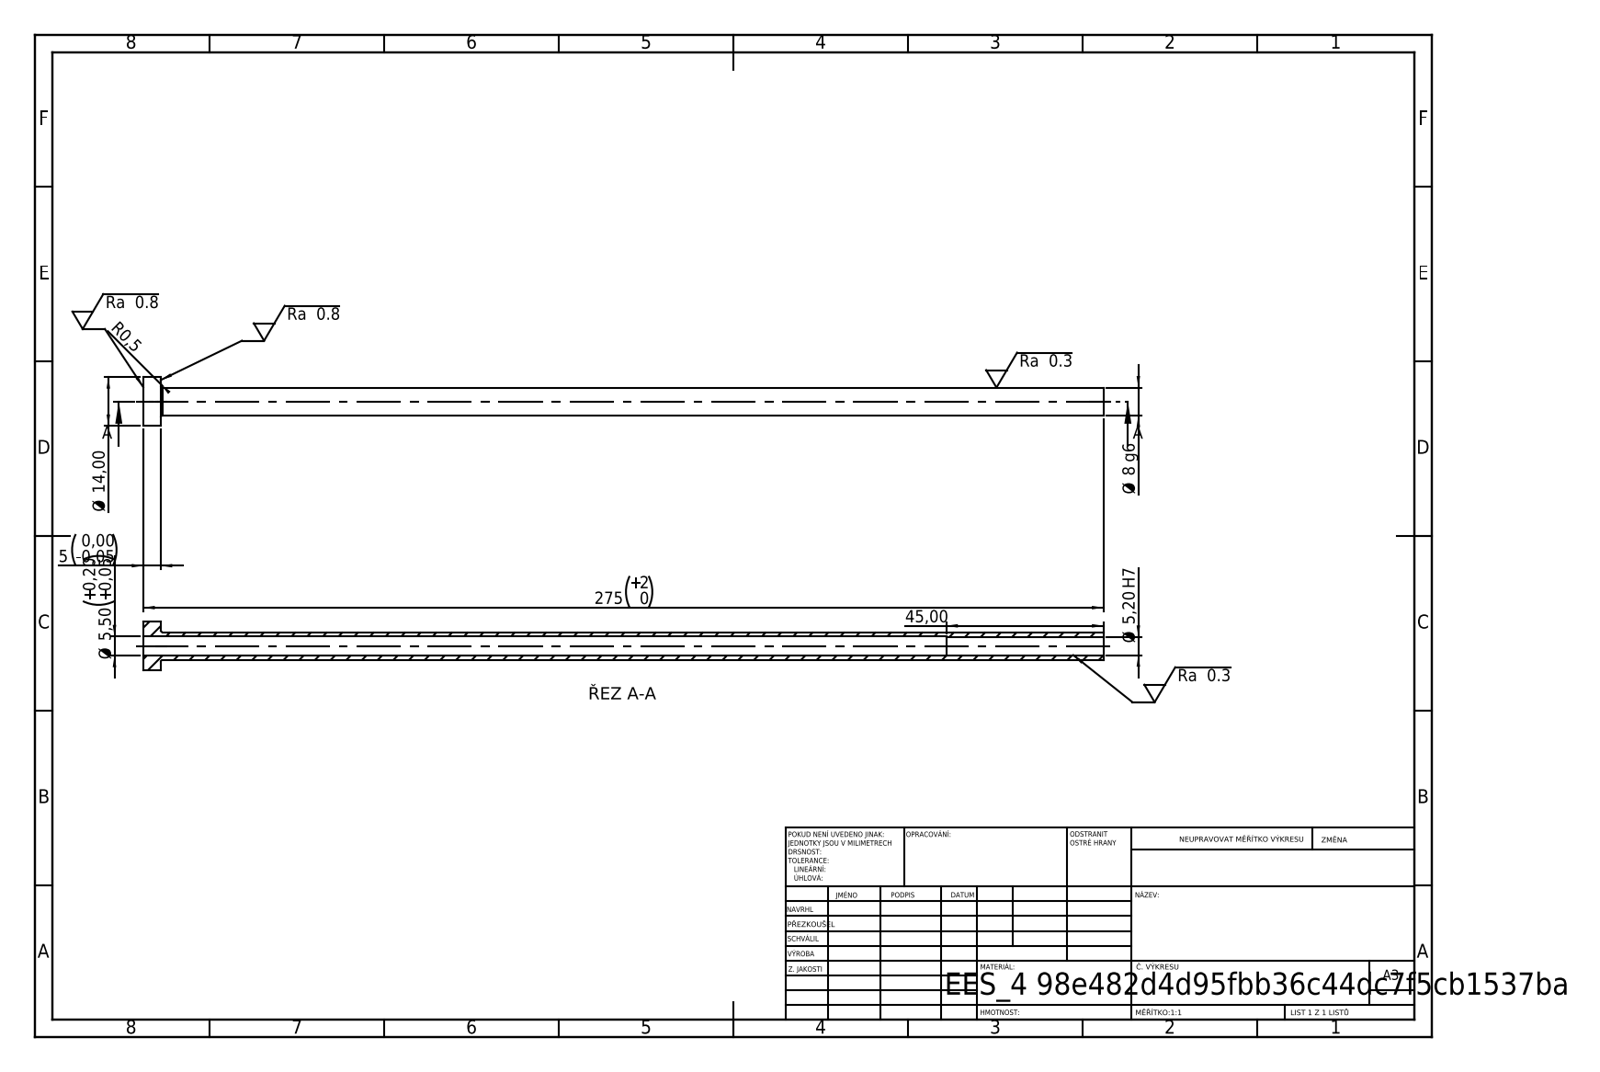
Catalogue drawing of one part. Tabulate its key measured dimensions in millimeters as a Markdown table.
| quantity | value |
| --- | --- |
| STEP written by | SolidWorks 2019 (CONFIG_CONTROL_DESIGN) |
| units | millimeters |
| bodies | 1 solid, 14 faces (4 planar, 8 cylindrical, 2 other) |
| overall size | 275 × 14 × 14 |
| volume | 7 923 mm³ |
| surface area | 11 975 mm² |
| round holes (diameter × count) | 5.2 × 1, 5.5 × 1 |
| round bosses / shafts (diameter × count) | 14 × 1, 8 × 1 |
| main face-to-face distances | 5, 275, 270, 230, 225, 45 |
